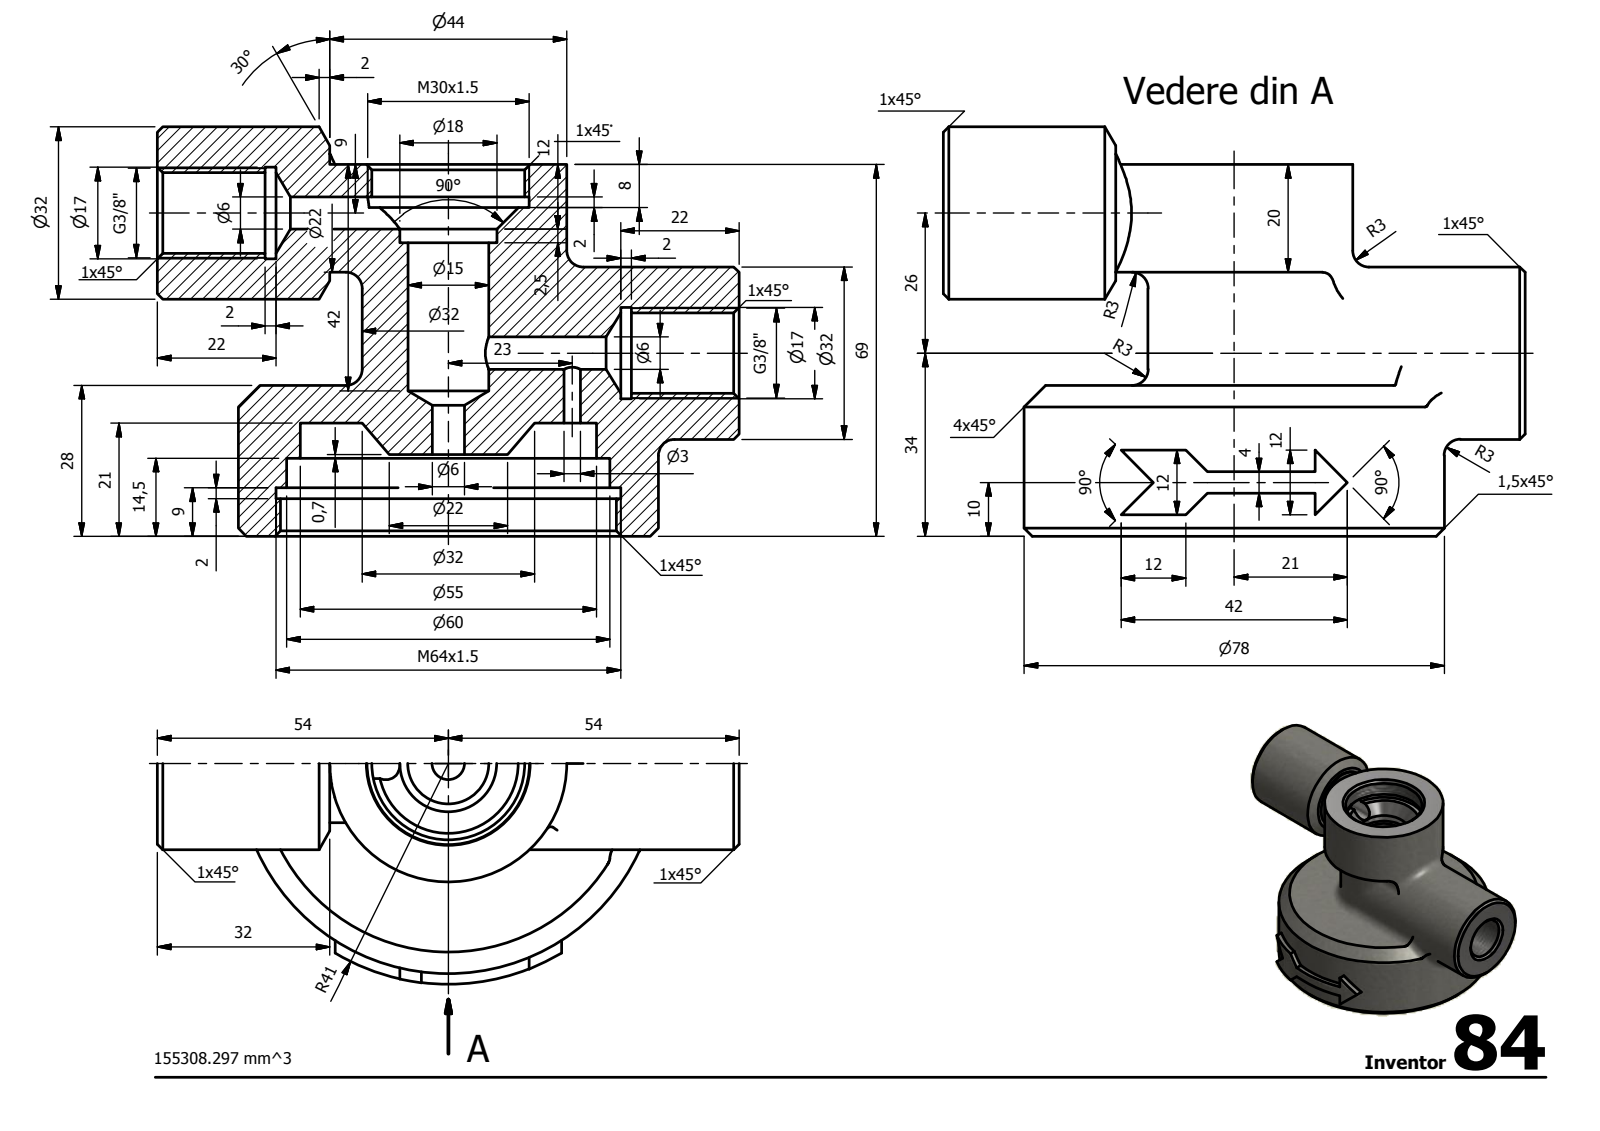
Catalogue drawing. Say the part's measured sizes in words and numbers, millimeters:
Its 3-D file was written by "Autodesk Inventor 2014 (AUTOMOTIVE_DESIGN)". It is 1 solid with 88 faces: 31 planar, 29 cylindrical and 28 other. Overall it measures 108 by 80 by 76 millimeters. Its volume is 155 309 cubic millimeters and its surface area 37 905 square millimeters. Round holes: 3 of diameter 6, 2 of diameter 14.95, 2 of diameter 17, 1 of diameter 3, 1 of diameter 15, 1 of diameter 18, 1 of diameter 28.38, 1 of diameter 30, 1 of diameter 44, 1 of diameter 55, 1 of diameter 60, 1 of diameter 62.38. Round bosses or shafts: 2 of diameter 32, 1 of diameter 78, 1 of diameter 22. Partial cylindrical surfaces (rounded edges, fillets, slot ends): 4 of radius 3, 1 of radius 16, 1 of radius 41. The main face-to-face distances are 7, 21, 28, 41, 69, 48, 12, 6.5, 40, 14.5. The hole center spacings are 23, 26.
